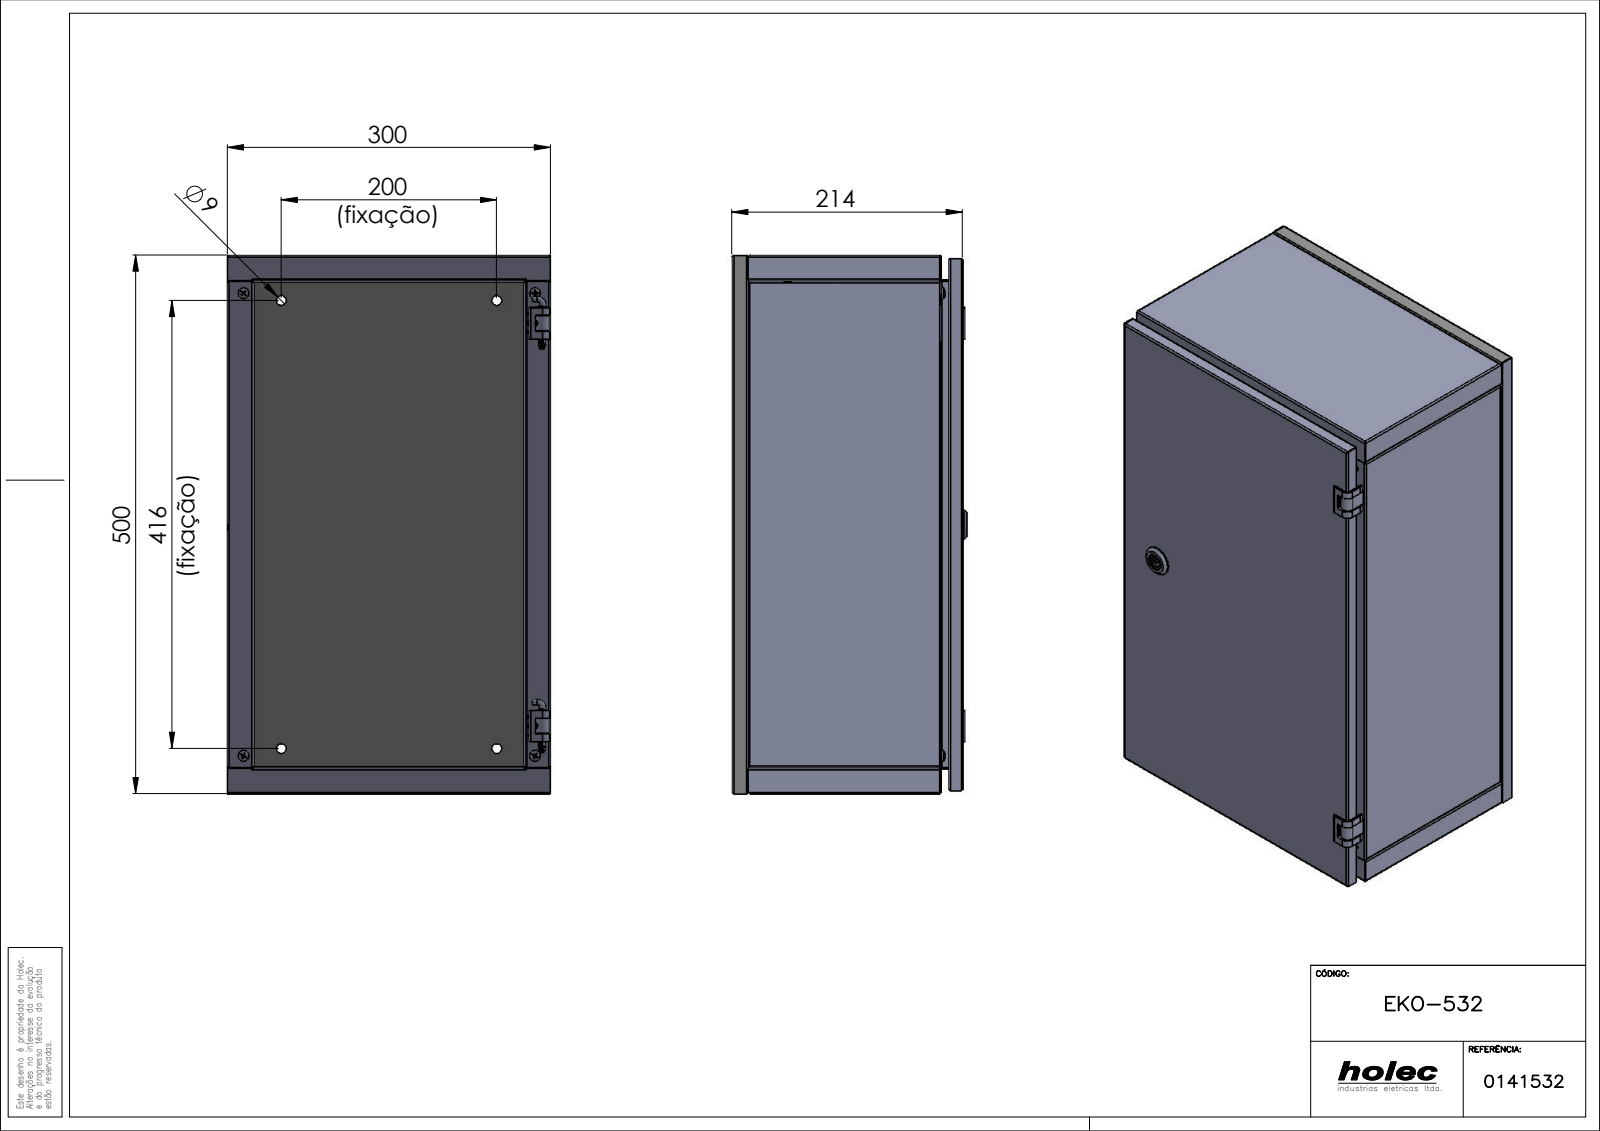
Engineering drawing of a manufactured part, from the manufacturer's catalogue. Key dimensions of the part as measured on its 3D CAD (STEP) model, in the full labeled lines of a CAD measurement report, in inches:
Part name (STEP PRODUCT): EKO-532
STEP written by: SolidWorks 2017 (AUTOMOTIVE_DESIGN)
Units: inches
Bodies: 52 solids, 2435 faces (1179 planar, 734 cylindrical, 522 other)
Overall size (bounding box): 19.685 × 11.811 × 8.587
Volume: 53.1 in³ · Surface area: 2 640 in²
Round holes (diameter × count): ⌀0.165 ×14, ⌀0.236 ×13, ⌀0.169 ×12, ⌀0.296 ×8, ⌀0.071 ×6, ⌀0.217 ×4, ⌀0.354 ×4, ⌀0.433 ×4, ⌀0.197 ×3, ⌀0.13 ×2, ⌀0.256 ×2, ⌀0.161 ×1
Round bosses / shafts (diameter × count): ⌀0.394 ×8, ⌀0.276 ×8, ⌀0.197 ×8, ⌀0.126 ×6, ⌀0.157 ×2, ⌀1.102 ×1, ⌀0.748 ×1, ⌀0.618 ×1
Partial cylindrical surfaces — rounded edges, fillets, slot ends (radius × count): R0.008 ×86, R0.059 ×49, R0.02 ×48, R0.012 ×20, R0.039 ×8, R0.079 ×5, R0.041 ×4, R0.098 ×4
Main face-to-face distances: 0.039, 8.39, 11.772, 8.429, 8.35, 19.646, 11.811, 11.732, 0.945, 0.902
Hole centre spacings: 0.984, 9.108, 1.969, 9.055, 9.267, 2.953, 9.524, 0.706
